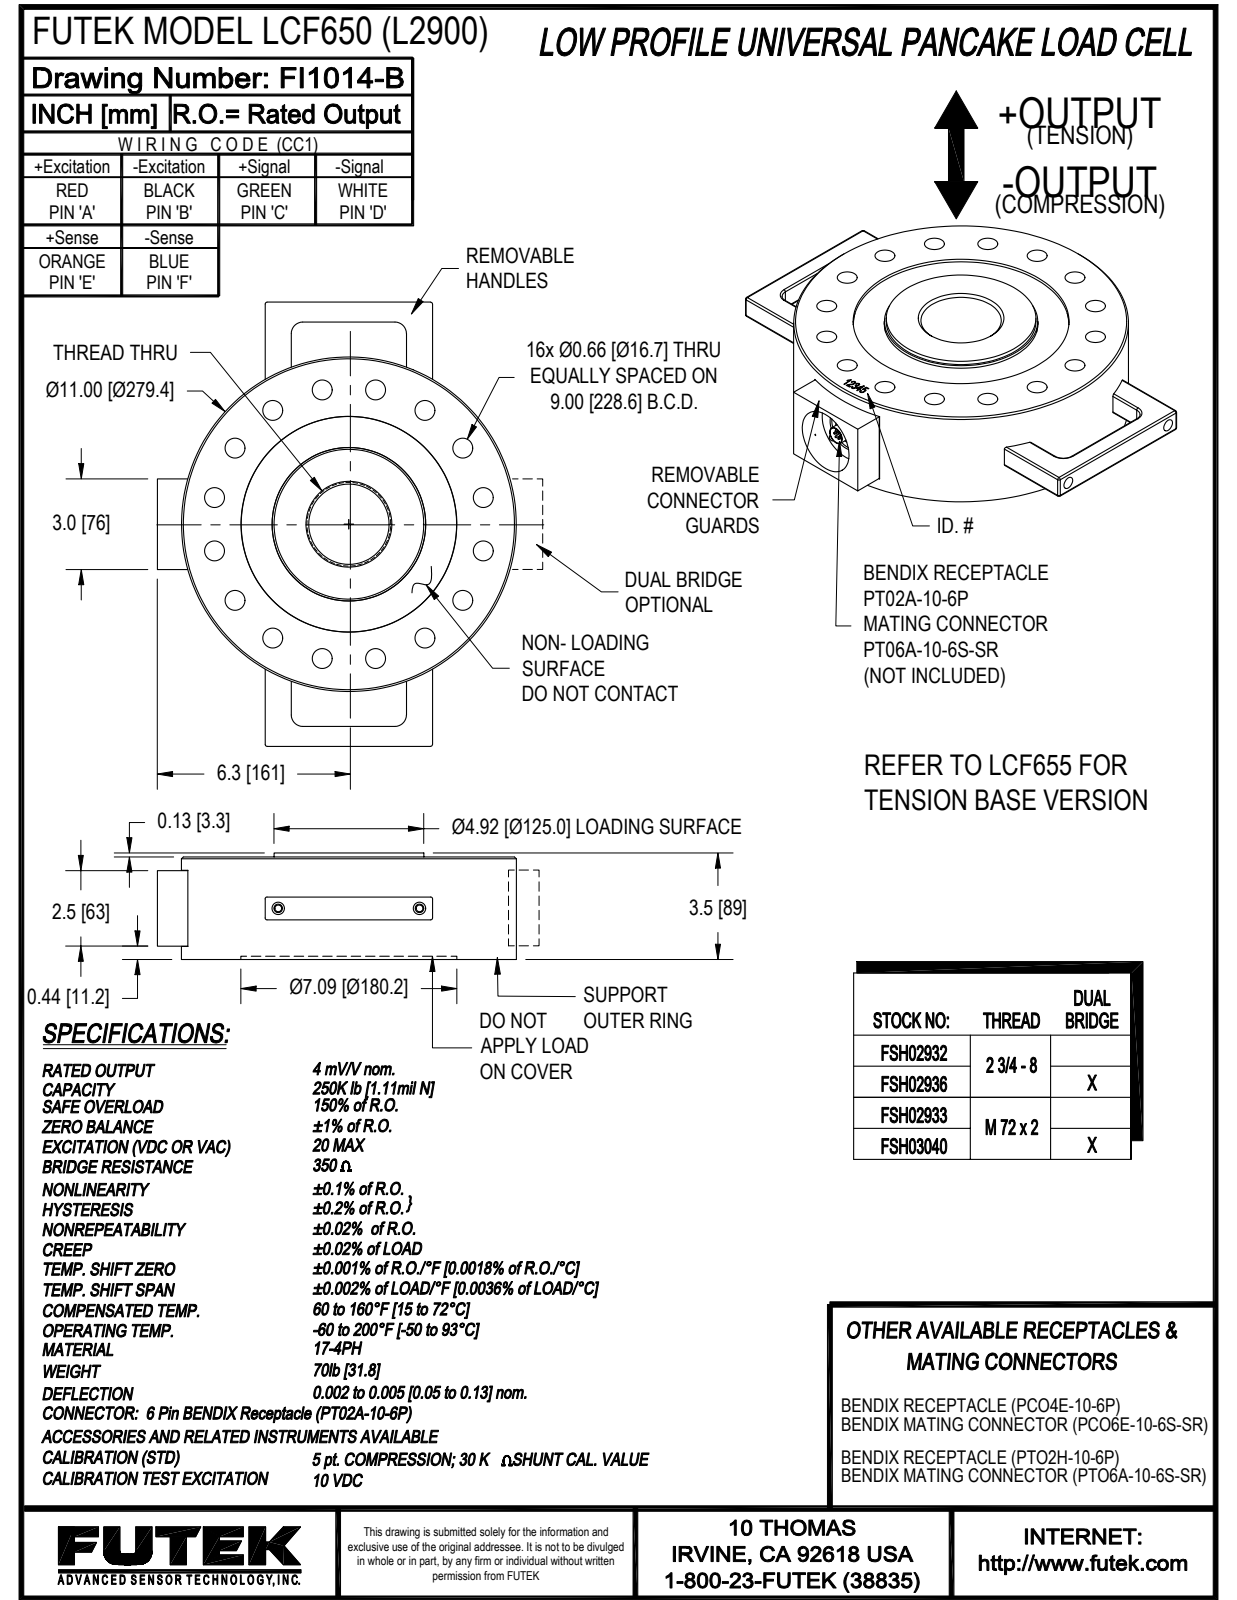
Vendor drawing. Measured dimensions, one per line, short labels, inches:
name: LCF650; ~~PART1
written by: Autodesk Inventor 2008 (AUTOMOTIVE_DESIGN)
unit: in
bodies: 1 solid, 411 faces (188 planar, 149 cylindrical, 74 other)
size: 14.502 × 11.881 × 3.5
volume: 289.2 in³; area: 521.3 in²
holes: 16× ⌀0.656, 4× ⌀0.094, 4× ⌀0.13, 4× ⌀0.164, 4× ⌀0.205, 4× ⌀0.22, 4× ⌀0.282, 4× ⌀0.41, 1× ⌀0.139, 1× ⌀0.187, 1× ⌀0.55, 1× ⌀0.625
bosses: 6× ⌀0.07, 6× ⌀0.06, 4× ⌀0.375, 4× ⌀0.312, 4× ⌀0.25, 4× ⌀0.19, 4× ⌀0.183, 4× ⌀0.112
rounds: 28× R0.063, 4× R0.05, 4× R0.375, 2× R5.5
face distances: 3.32, 3.265, 0.105, 0.055, 3.215, 3.16, 0.05, 3.37, 3.5, 3.45
hole spacings: 8.315, 1.756, 3.444, 4.5, 8.827, 0.919, 1.3, 5
